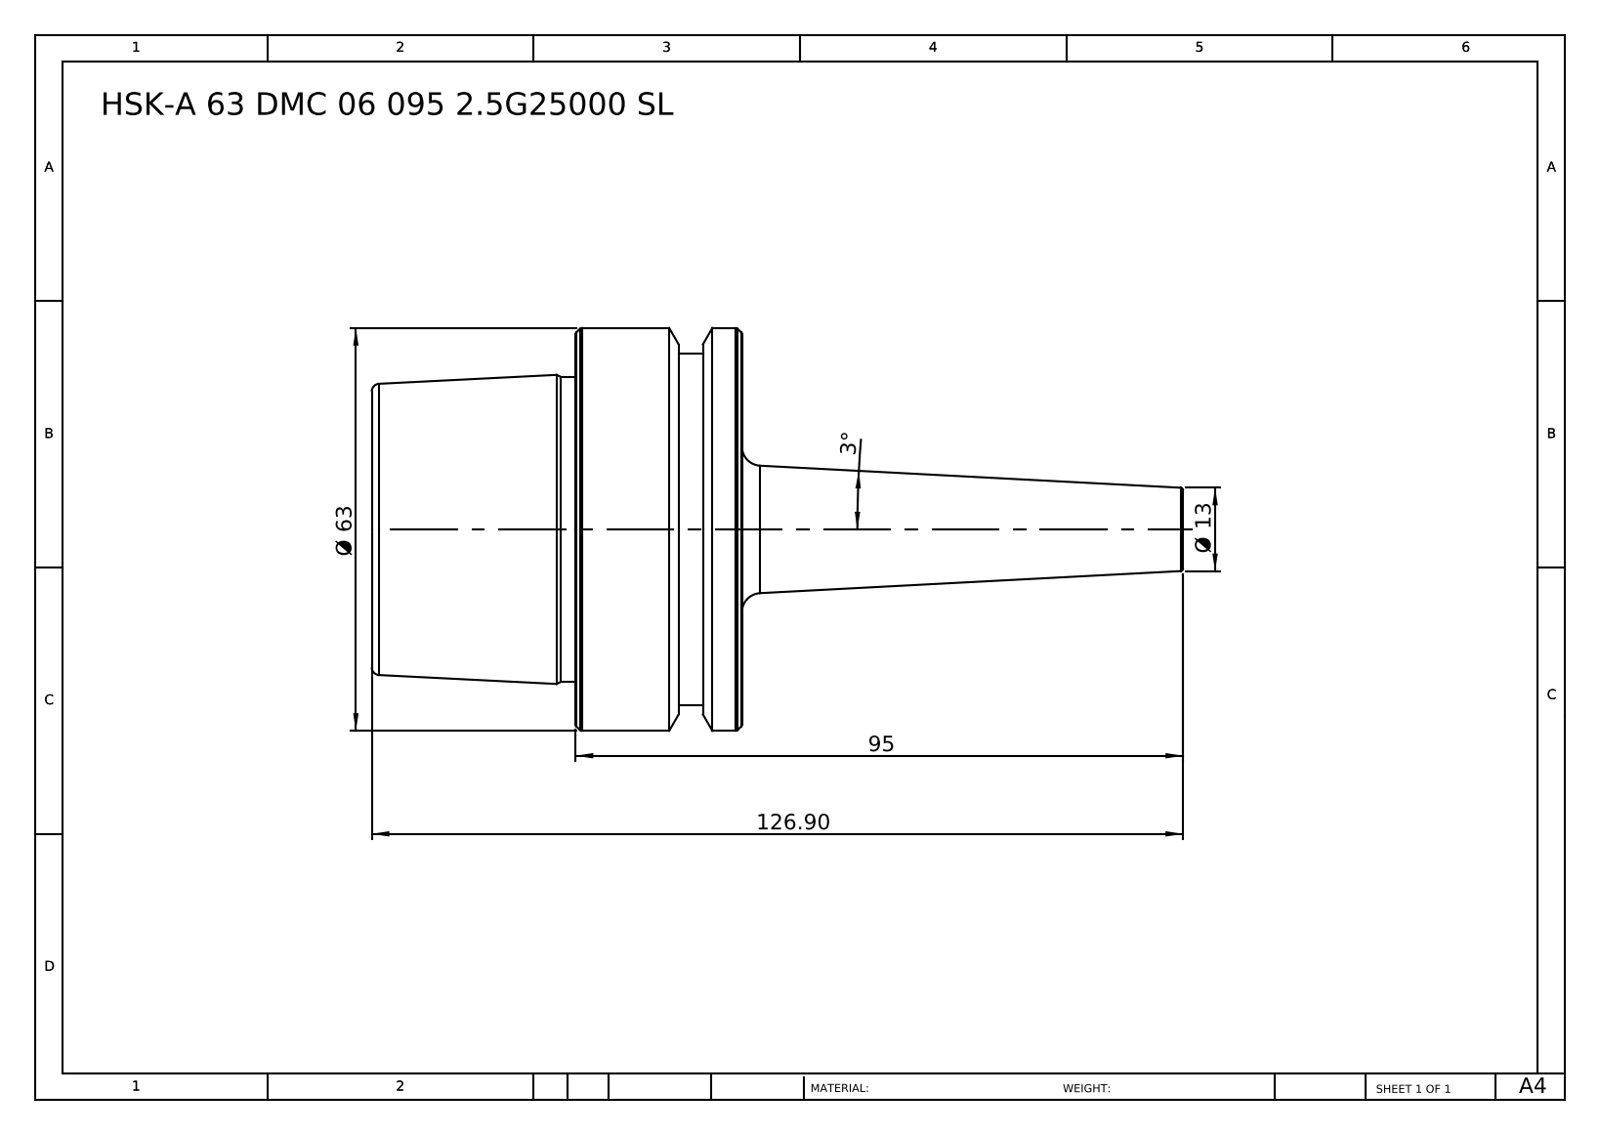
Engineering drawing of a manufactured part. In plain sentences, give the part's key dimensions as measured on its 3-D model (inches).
The part is named "HSK-A 63 DMC 06 095 2.5G25000 SL". Its 3-D file was written by "SolidWorks 2014 (CONFIG_CONTROL_DESIGN)". It is 1 solid with 46 faces: 6 planar, 8 cylindrical and 32 other. Overall it measures 4.996 by 2.48 by 2.48 inches. Its volume is 9.024 cubic inches and its surface area 30.98 square inches. Round bosses or shafts: 1 of diameter 2.48, 1 of diameter 2.165, 1 of diameter 1.881. The main face-to-face distances are 2.28, 1.024, 1.256, 0.24, 0.783, 2.039, 0.39, 0.15, 0.634, 1.89.
